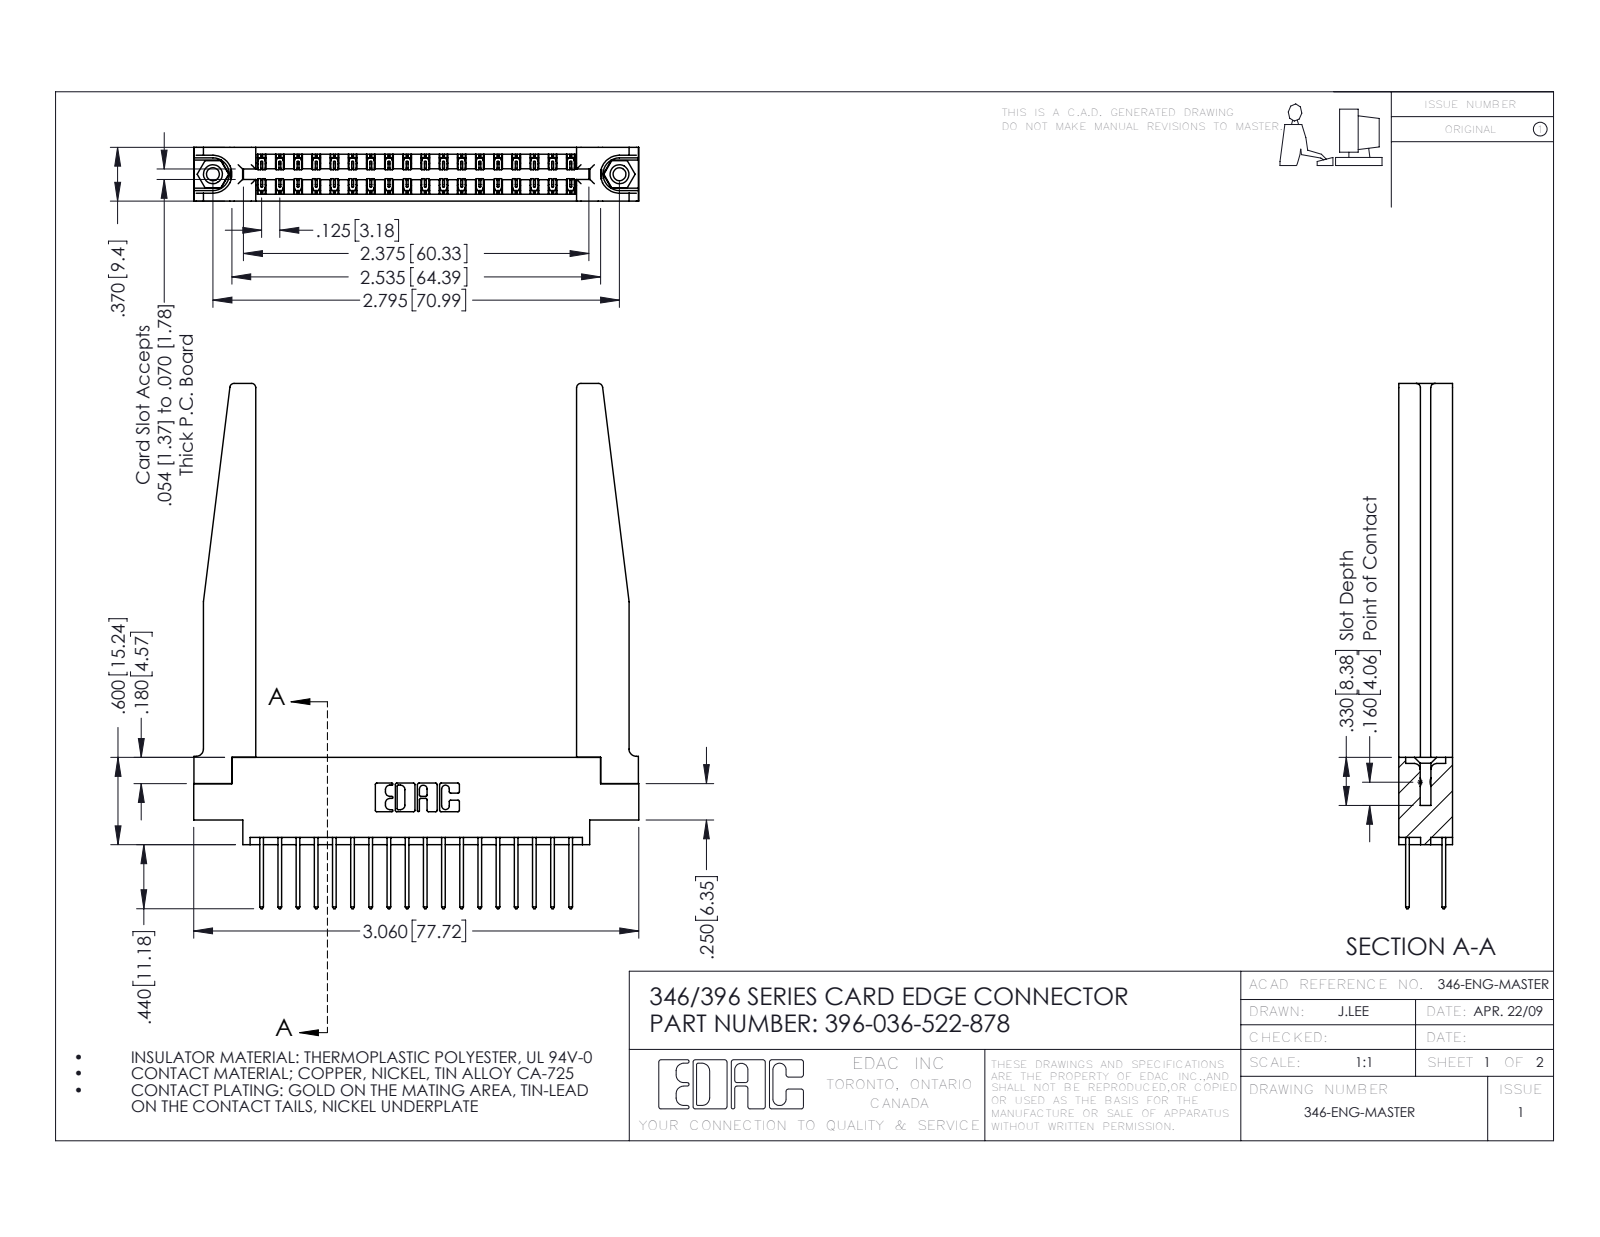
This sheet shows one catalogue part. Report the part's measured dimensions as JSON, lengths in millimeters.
{"part_name": "396-036-522-878; 346 Part_0.170 Offset - 0.156 Dia-TH; 345-292-001_345-293-122; 346-220-078_345-220-078 (+1 more)", "step_written_by": "SolidWorks 2016 (CONFIG_CONTROL_DESIGN)", "units": "millimeters", "bodies": {"solids": 41, "faces": 2232, "planar": 1482, "cylindrical": 698, "other": 52}, "overall_size": [91.7, 77.7, 9.4], "volume_mm3": 14200, "surface_area_mm2": 16850, "round_holes": [[2.3, 2], [3.2, 2], [4, 2], [1.6, 1]], "round_bosses_or_shafts": [[3.9, 2]], "partial_cylinders_radius": [[0.2, 54], [0.3, 36], [0.3, 22], [0.8, 8], [0.2, 6], [0.8, 6], [0.7, 3], [0.4, 2]], "face_to_face_distances": [9.4, 1.2, 8.2, 1.8, 3.8, 3.8, 6.4, 7.6, 0.6, 7], "hole_center_spacings": [6.2, 65.7, 71]}
